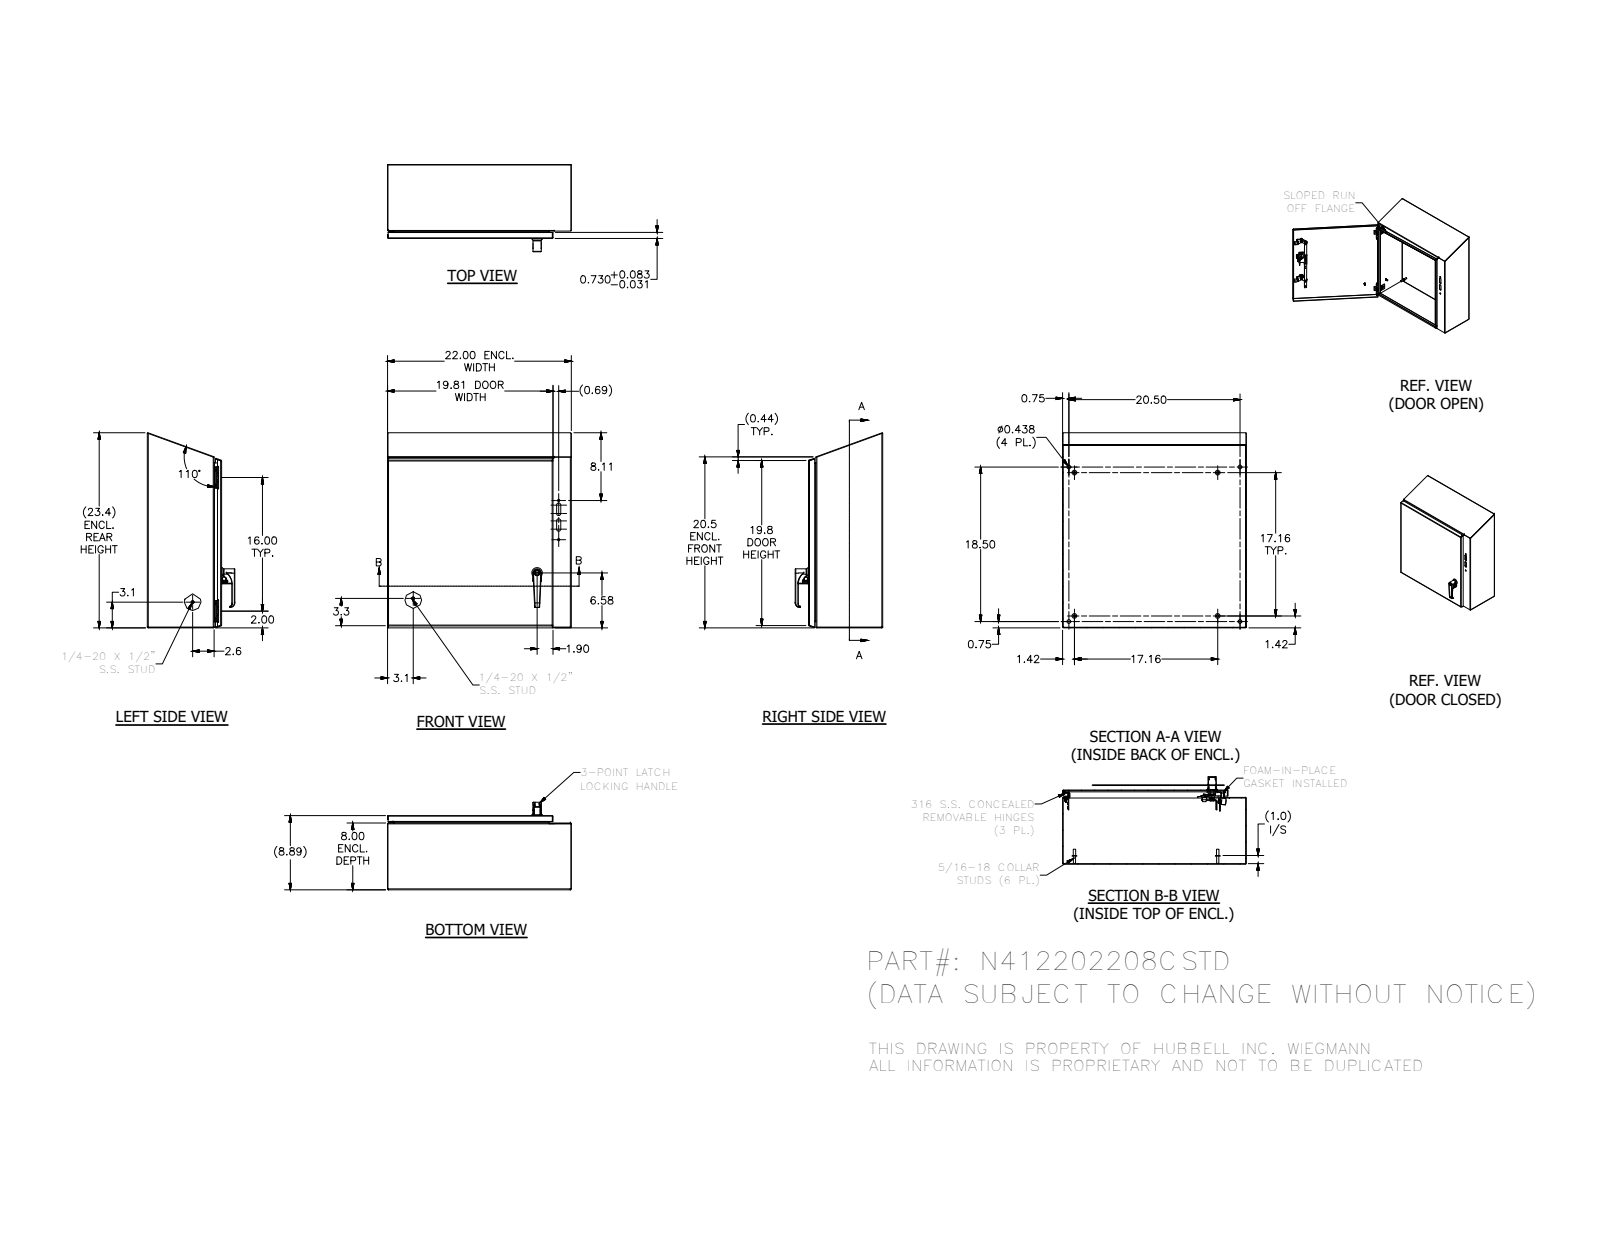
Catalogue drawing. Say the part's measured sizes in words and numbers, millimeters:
The part is named "N412202208CSTD". Its 3-D file was written by "SolidWorks 2018 (AUTOMOTIVE_DESIGN)". It is 63 solids with 2117 faces: 839 planar, 749 cylindrical and 529 other. Overall it measures 593.5 by 558.8 by 266.2 millimeters. Its volume is 2 320 000 cubic millimeters and its surface area 2 448 000 square millimeters. Round holes: 5 of diameter 4, 4 of diameter 2.4, 4 of diameter 3.7, 4 of diameter 3.9, 4 of diameter 4.2, 4 of diameter 4.4, 4 of diameter 4.7, 4 of diameter 11.1, 3 of diameter 8.1, 2 of diameter 5, 2 of diameter 5.4, 2 of diameter 5.6. Round bosses or shafts: 12 of diameter 6.4, 8 of diameter 7.6, 4 of diameter 14.3, 4 of diameter 11.1, 4 of diameter 9.1, 4 of diameter 8.1, 4 of diameter 6.5, 4 of diameter 4.8. Partial cylindrical surfaces (rounded edges, fillets, slot ends): 38 of radius 0.5, 31 of radius 0.3, 29 of radius 0.8, 26 of radius 1.3, 25 of radius 3.2, 19 of radius 2.7, 18 of radius 0.4, 16 of radius 0.6. The main face-to-face distances are 1.9, 223.9, 222, 225.7, 556.9, 201.3, 22.5, 555, 558.8, 20.7. The hole center spacings are 406.4, 12.7, 269.9, 530.1, 16.7, 16.8, 25, 33.2.
